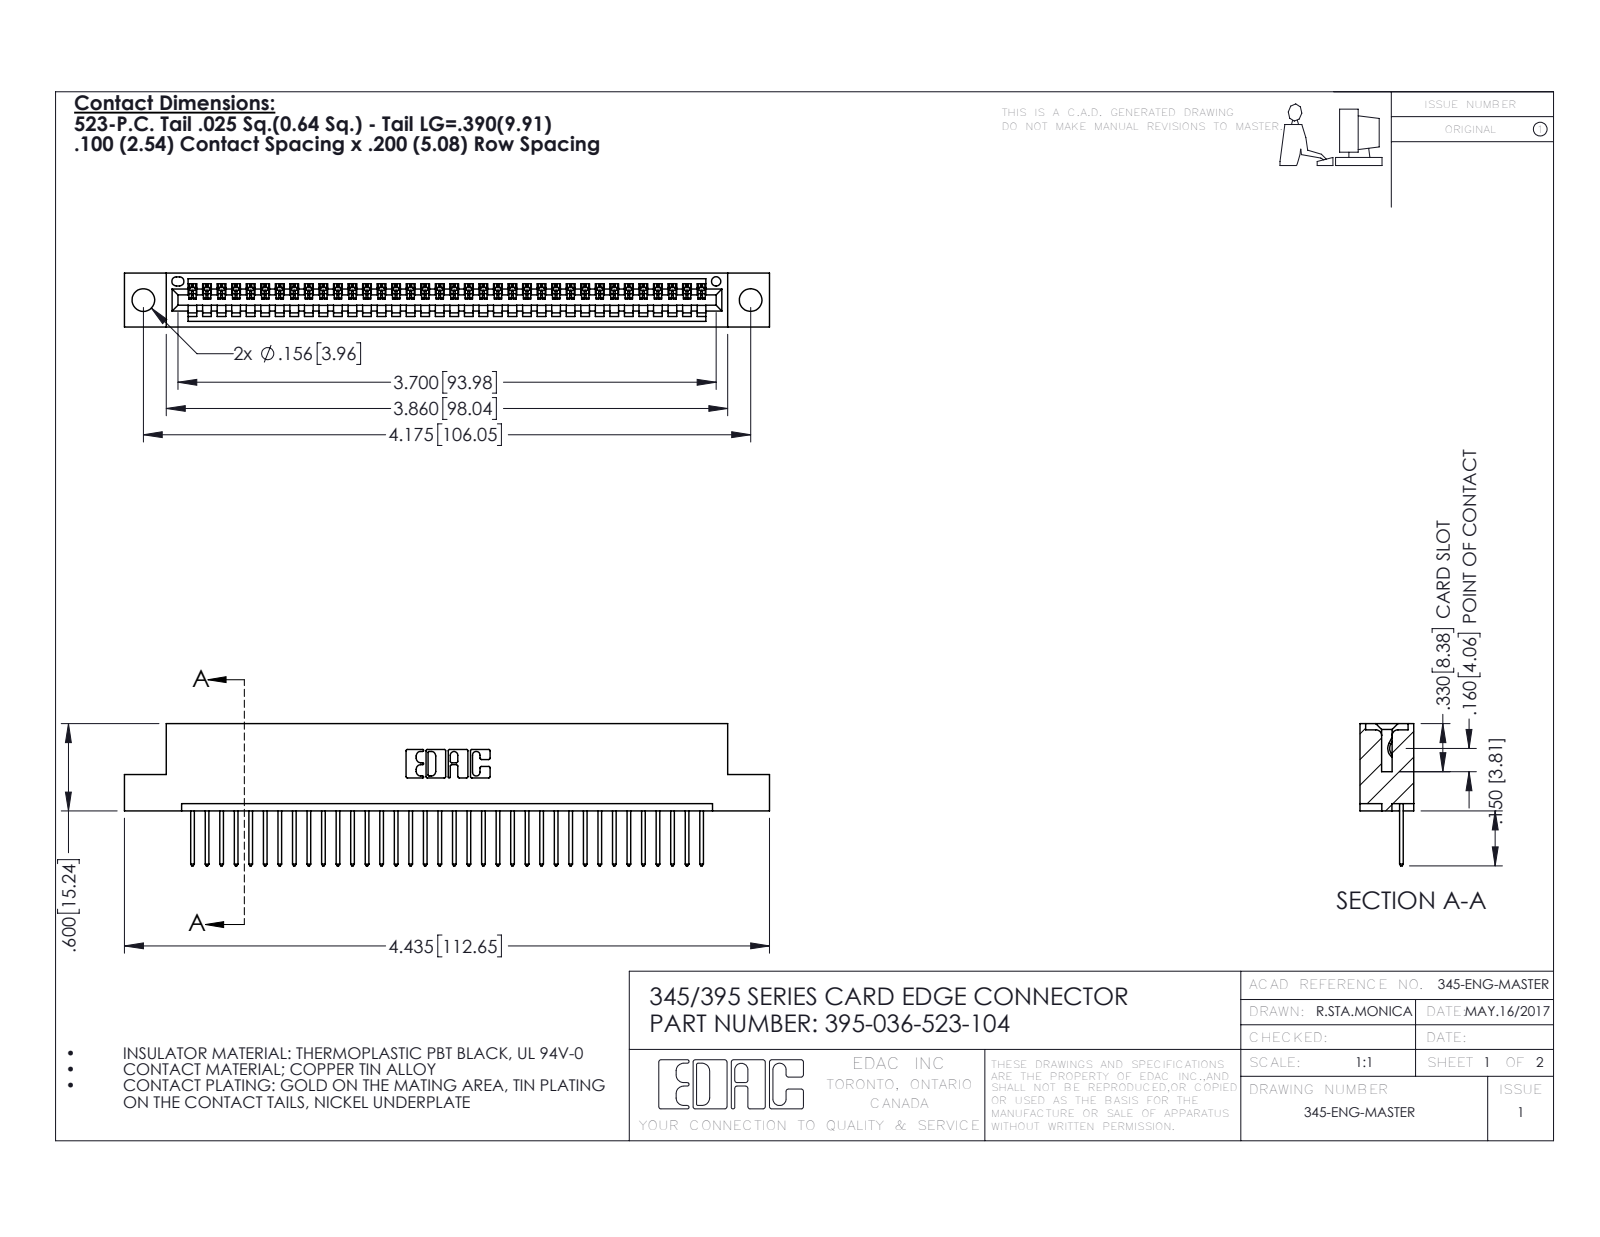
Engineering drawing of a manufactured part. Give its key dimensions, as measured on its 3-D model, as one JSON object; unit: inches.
{"part_name": "395-036-523-104; 345 Part_Flush Mounting Lugs - 0.156 Dia-TH; 345-292-001_345-293-123", "step_written_by": "SolidWorks 2016 (CONFIG_CONTROL_DESIGN)", "units": "inches", "bodies": {"solids": 37, "faces": 2214, "planar": 1520, "cylindrical": 694, "other": 0}, "overall_size": [4.435, 0.977, 0.37], "volume_in3": 0.644, "surface_area_in2": 21.37, "round_holes": [[0.156, 2], [0.064, 1]], "partial_cylinders_radius": [[0.006, 72], [0.01, 72], [0.01, 22], [0.007, 6], [0.031, 6], [0.026, 3], [0.031, 2], [0.04, 2]], "face_to_face_distances": [0.298, 0.072, 0.37, 0.2, 0.098, 0.272, 0.025, 0.225, 0.149, 0.072], "hole_center_spacings": [0.27, 3.939, 4.175]}
